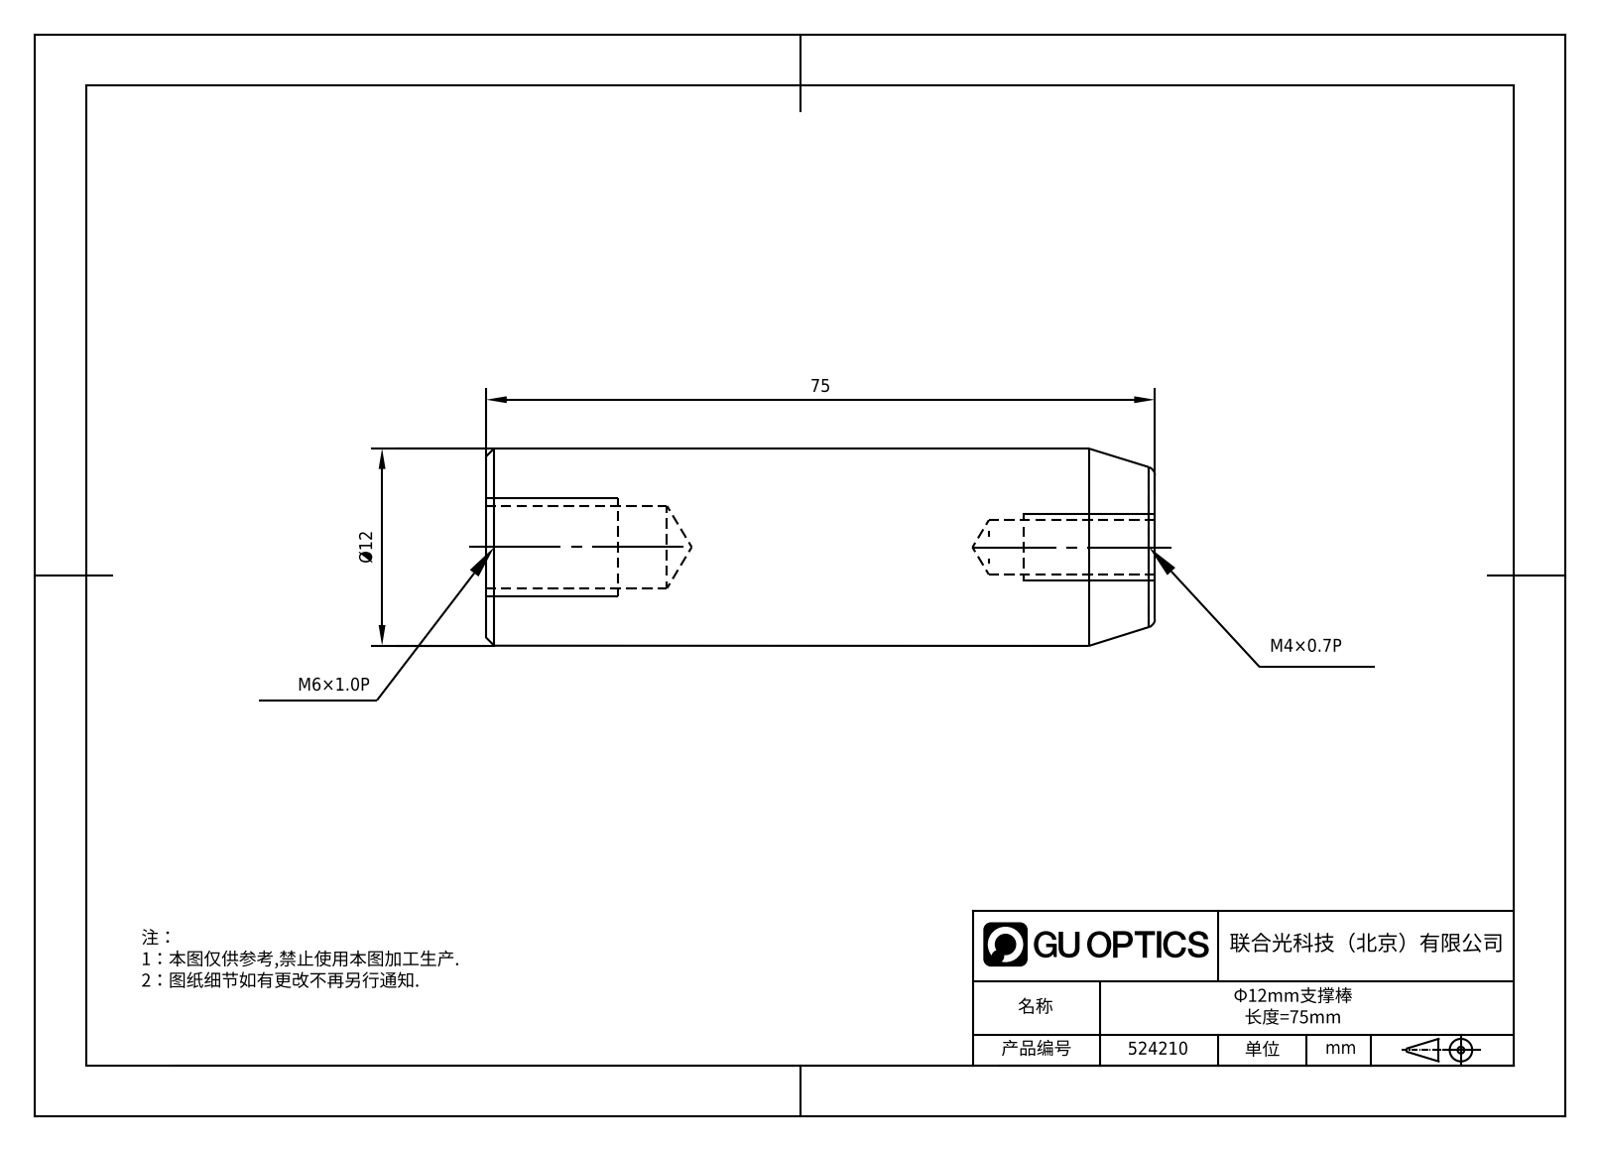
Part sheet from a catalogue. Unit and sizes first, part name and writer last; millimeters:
Units: millimetres
Overall size (bounding box): 75 × 12 × 12
Round holes (diameter × count): ⌀3.3 ×1, ⌀5 ×1
Round bosses / shafts (diameter × count): ⌀12 ×1
Main face-to-face distances: 75
Volume: 8 074 mm³ · Surface area: 3 270 mm²
Bodies: 1 solid, 10 faces (2 planar, 3 cylindrical, 5 other)
Part name (STEP PRODUCT): 524210
STEP written by: SolidWorks 2020 (CONFIG_CONTROL_DESIGN)
